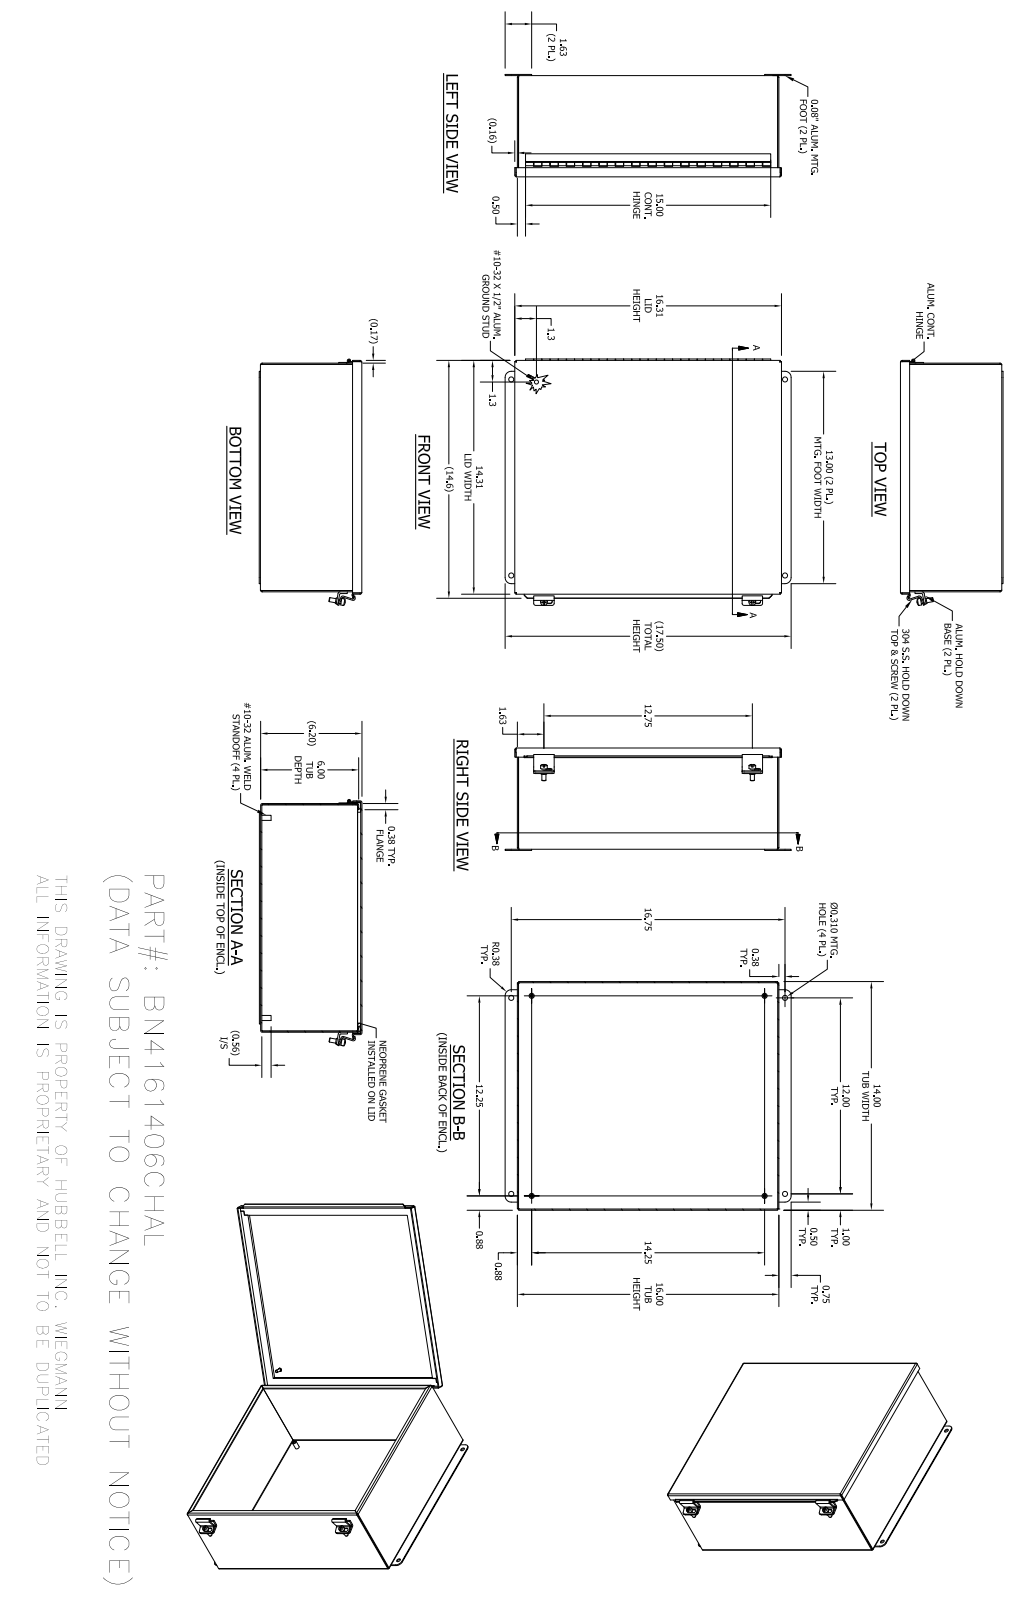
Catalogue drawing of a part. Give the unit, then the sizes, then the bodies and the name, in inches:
Units: inches
Overall size (bounding box): 17.5 × 15.086 × 6.274
Round holes (diameter × count): ⌀0.156 ×4, ⌀0.25 ×4, ⌀0.31 ×4, ⌀0.196 ×2, ⌀0.117 ×1
Round bosses / shafts (diameter × count): ⌀0.25 ×5, ⌀0.313 ×4, ⌀0.409 ×2, ⌀0.344 ×2, ⌀0.2 ×1, ⌀0.19 ×1, ⌀0.1 ×1
Partial cylindrical surfaces — rounded edges, fillets, slot ends (radius × count): R0.031 ×13, R0.105 ×13, R0.125 ×8, R0.133 ×4, R0.375 ×4, R0.063 ×3, R0.126 ×3
Main face-to-face distances: 0.074, 6.125, 6.199, 6.051, 13.926, 15.926, 14, 13.852, 16, 15.852
Hole centre spacings: 12.189, 1.256, 12.25, 15.5, 15.5, 18.792, 19.679, 19.679
Volume: 75.24 in³ · Surface area: 1 984 in²
Bodies: 20 solids, 483 faces (297 planar, 145 cylindrical, 41 other)
Part name (STEP PRODUCT): B_161406_ALBKP; 32845TH; 32845LH; 32845P (+8 more)
STEP written by: Autodesk Inventor 2016 (AUTOMOTIVE_DESIGN)
